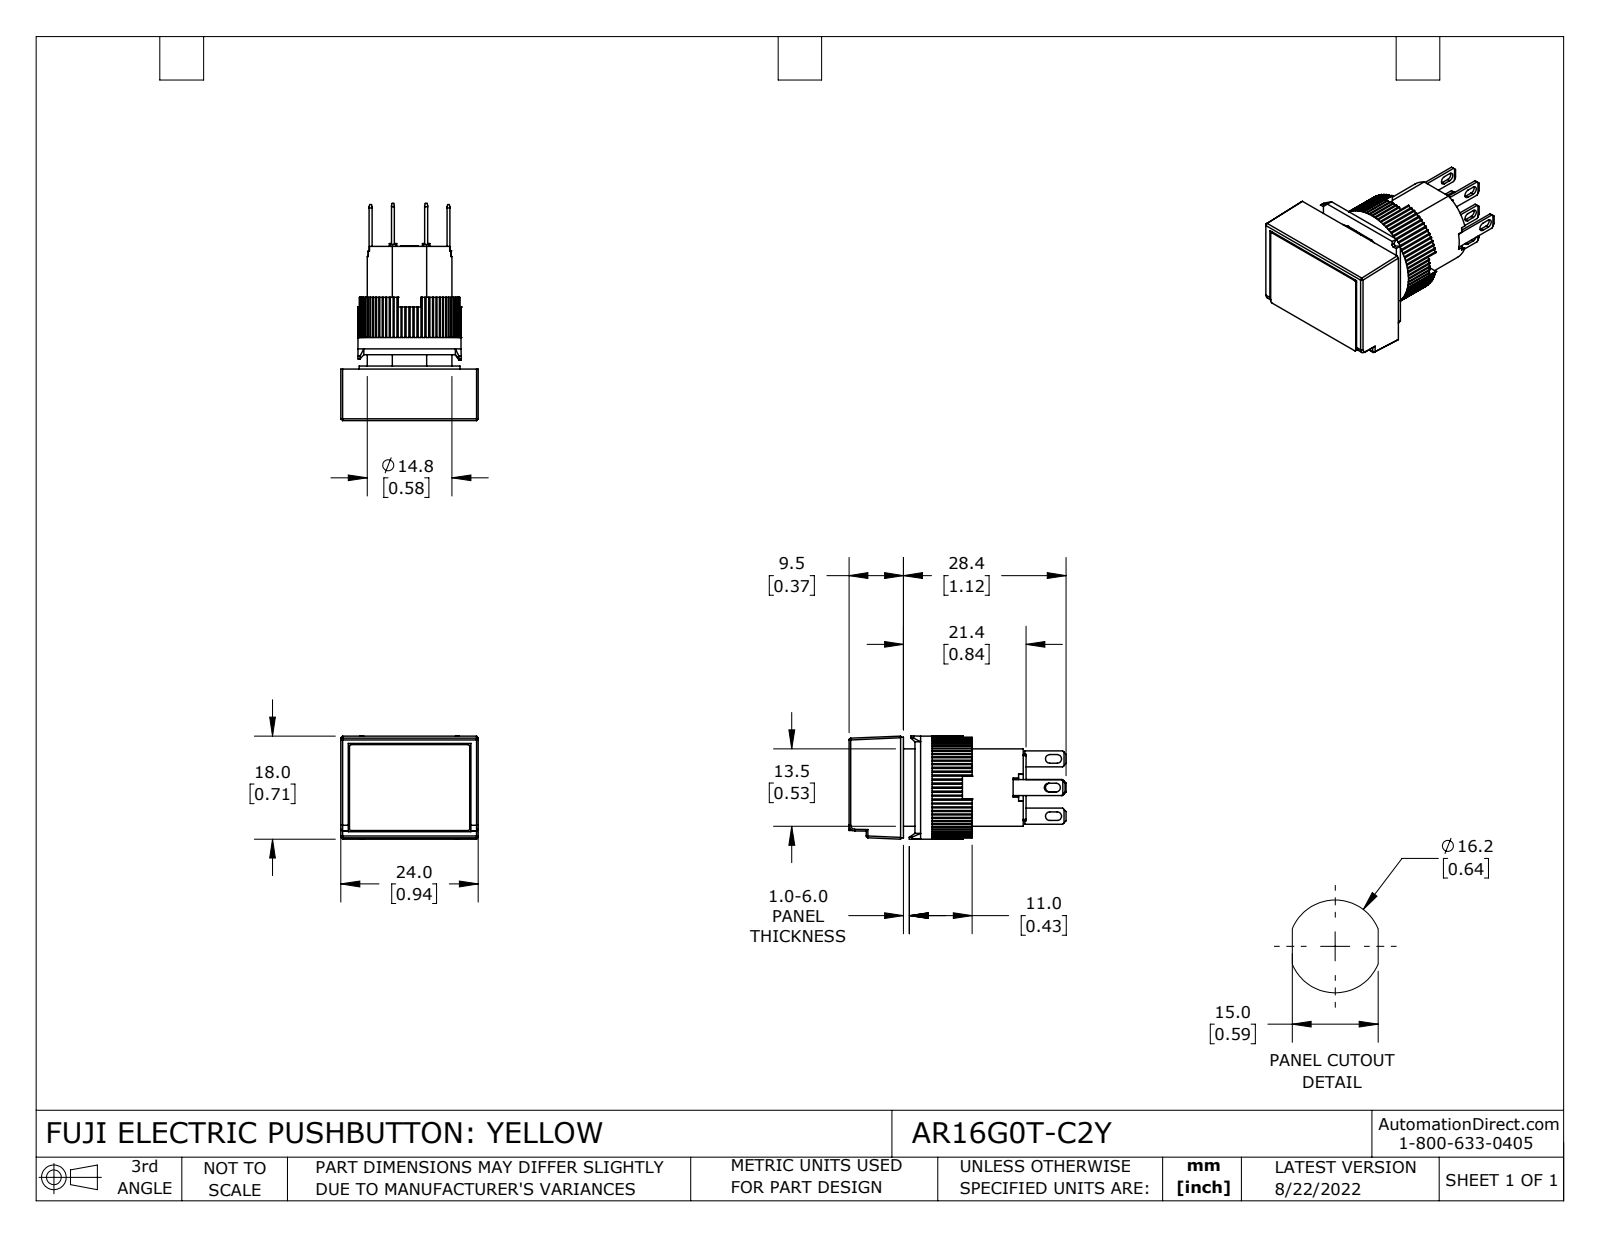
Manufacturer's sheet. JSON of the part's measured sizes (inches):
{"part_name": "AR16G0T-C2Y", "step_written_by": "SolidWorks 2021 (CONFIG_CONTROL_DESIGN)", "units": "inches", "bodies": {"solids": 14, "faces": 841, "planar": 654, "cylindrical": 181, "other": 6}, "overall_size": [1.492, 0.945, 0.709], "volume_in3": 0.448, "surface_area_in2": 9.503, "round_holes": [[0.543, 1], [0.583, 1]], "round_bosses_or_shafts": [[0.709, 1], [0.693, 1]], "partial_cylinders_radius": [[0.01, 80], [0.008, 12], [0.03, 8], [0.012, 6], [0.039, 1]], "face_to_face_distances": [0.213, 0.354, 0.142, 0.35, 0.492, 0.138, 0.02, 0.843, 0.059, 0.453]}
